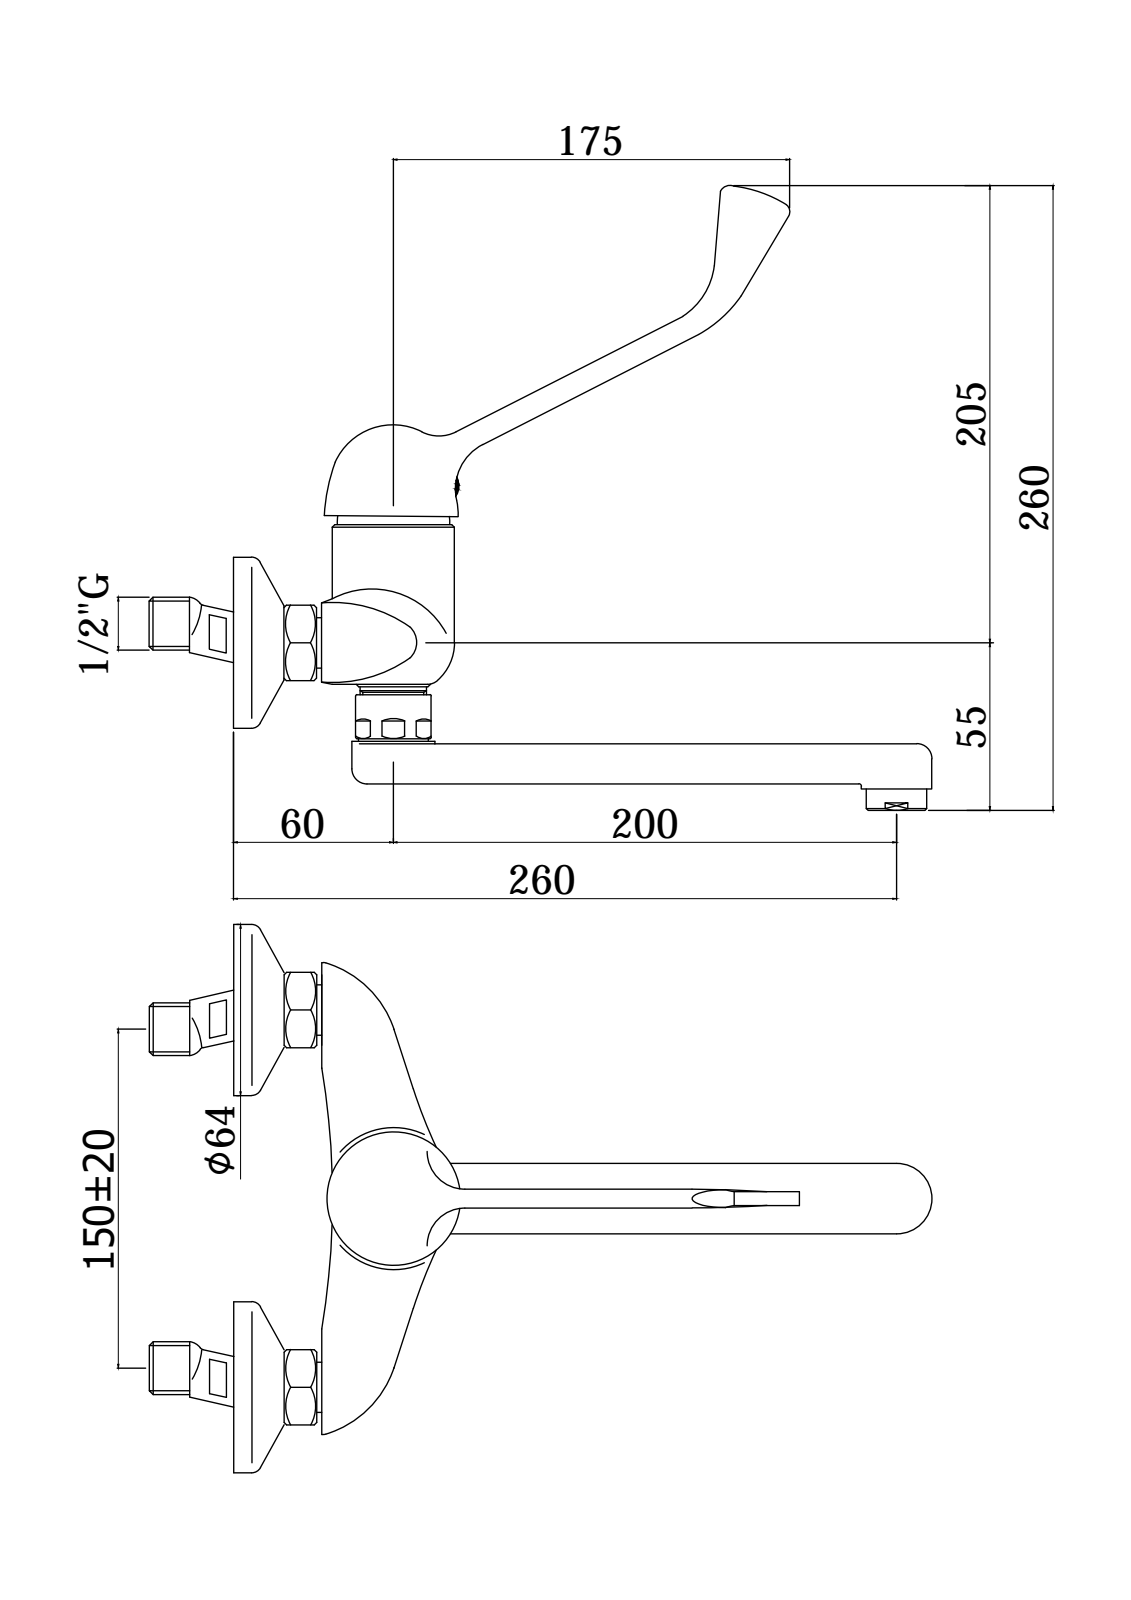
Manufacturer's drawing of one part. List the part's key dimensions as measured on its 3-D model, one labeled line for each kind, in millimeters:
Part name (STEP PRODUCT): ND302CR
STEP written by: CREO PARAMETRIC BY PTC INC, 2020044 (CONFIG_CONTROL_DESIGN)
Units: millimetres
Bodies: 2 solids, 349 faces (96 planar, 87 cylindrical, 166 other)
Overall size (bounding box): 286.2 × 277.5 × 215.5
Volume: 455 159 mm³ · Surface area: 107 045 mm²
Round holes (diameter × count): ⌀26 ×2, ⌀5 ×1, ⌀6 ×1, ⌀14.9 ×1, ⌀16.5 ×1, ⌀17.3 ×1, ⌀18.2 ×1, ⌀18.5 ×1, ⌀20 ×1, ⌀21 ×1, ⌀21.2 ×1, ⌀23 ×1
Round bosses / shafts (diameter × count): ⌀65.5 ×2, ⌀28 ×2, ⌀24 ×2, ⌀50 ×1, ⌀30 ×1, ⌀26.4 ×1, ⌀21 ×1, ⌀10 ×1
Partial cylindrical surfaces — rounded edges, fillets, slot ends (radius × count): R3 ×2, R5 ×2, R7 ×2, R8 ×2, R15.5 ×2, R20.5 ×2, R18 ×1, R392.45 ×1
Main face-to-face distances: 1, 15, 14, 16, 6, 35.5, 29, 1.5, 10.8, 2
Hole centre spacings: 200
